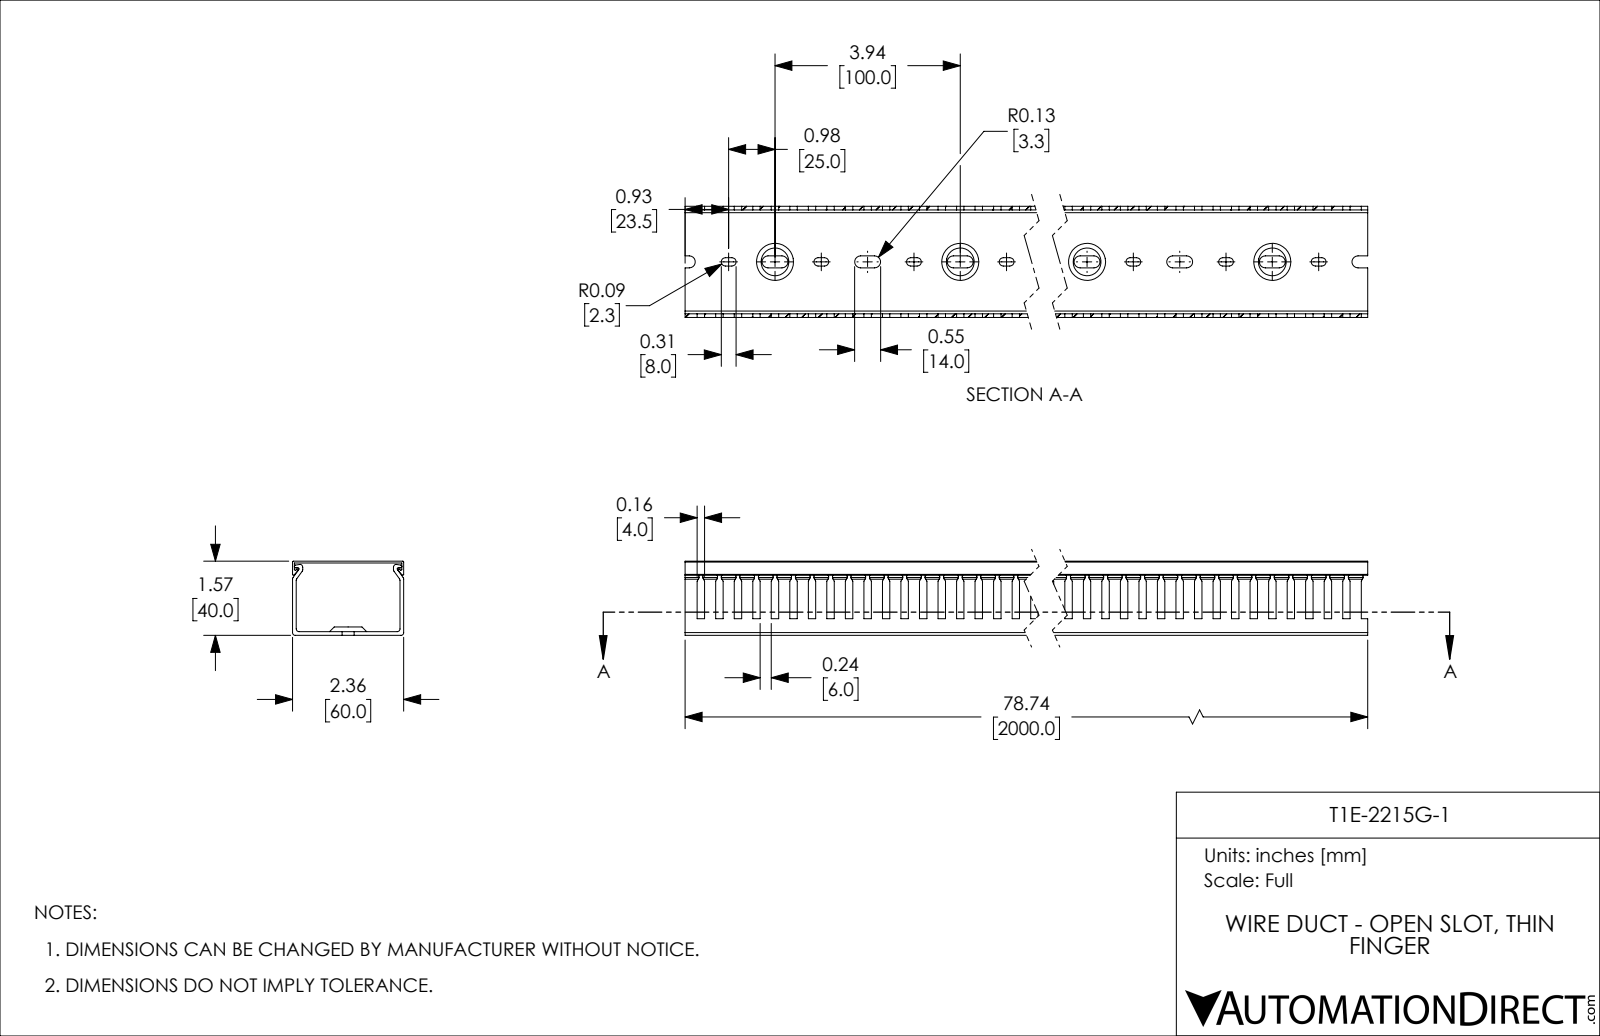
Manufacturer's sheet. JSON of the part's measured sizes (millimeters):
{"part_name": "T1E-2215G-1", "step_written_by": "SolidWorks 2021 (CONFIG_CONTROL_DESIGN)", "units": "millimeters", "bodies": {"solids": 2, "faces": 1005, "planar": 534, "cylindrical": 431, "other": 40}, "overall_size": [2000, 60, 40], "volume_mm3": 704820, "surface_area_mm2": 859894, "partial_cylinders_radius": [[2.25, 80], [3.25, 80], [1.5, 12], [0.5, 8], [0.75, 6]], "face_to_face_distances": [2, 1, 40, 58, 39, 37, 38, 60, 56, 59]}
